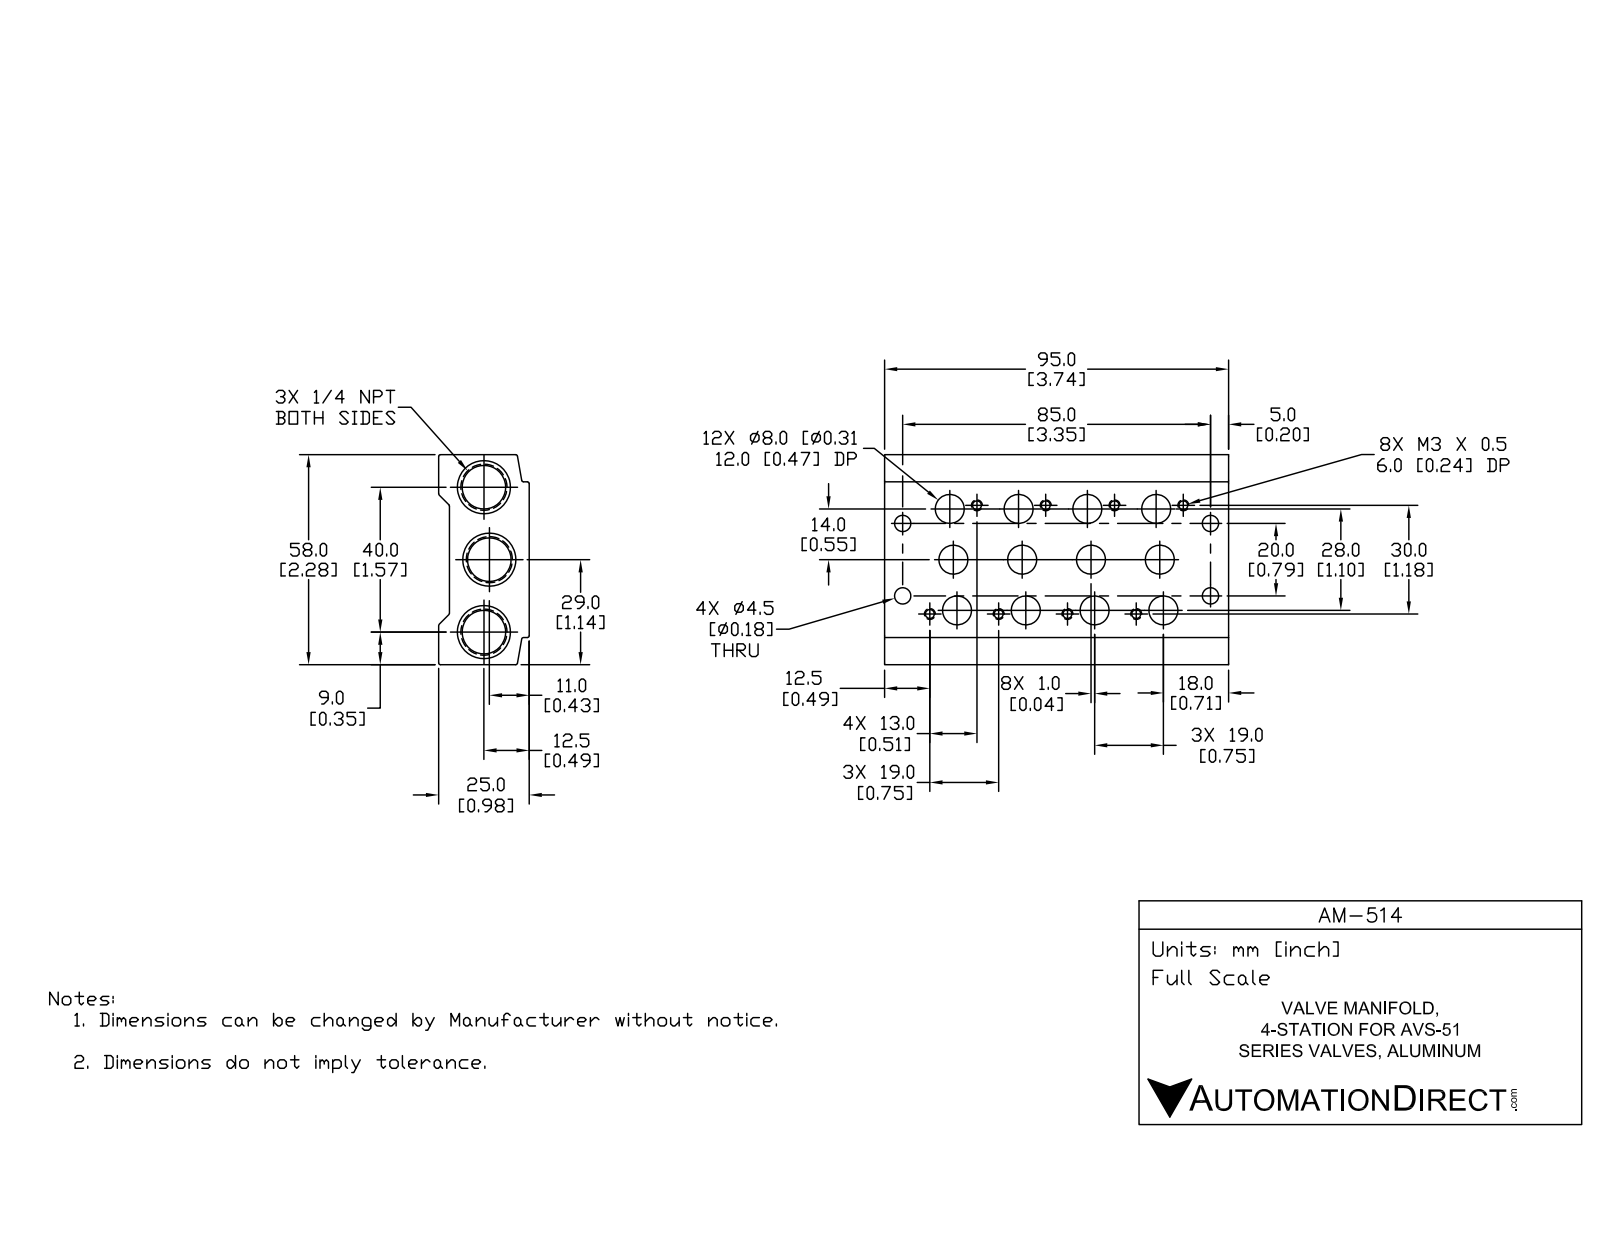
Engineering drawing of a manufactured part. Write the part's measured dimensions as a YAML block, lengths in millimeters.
part_name: "AM-514"
step_written_by: "SolidWorks 2015 (CONFIG_CONTROL_DESIGN)"
units: millimeters
bodies: {solids: 1, faces: 121, planar: 28, cylindrical: 65, other: 28}
overall_size: [95, 58, 25]
volume: 88334
surface_area: 31024
round_holes:
  - {diameter: 2.5, count: 8}
  - {diameter: 6.5, count: 8}
  - {diameter: 4.5, count: 4}
  - {diameter: 10.2, count: 4}
  - {diameter: 11.13, count: 3}
partial_cylinders:
  - {radius: 0.5, count: 11}
face_to_face_distances: [22, 58, 3, 25, 95, 10.02, 84.98, 6, 52, 15]
hole_center_spacings: [19, 38, 7.57, 14.04, 16.35, 29.52, 11.54, 19.53]
